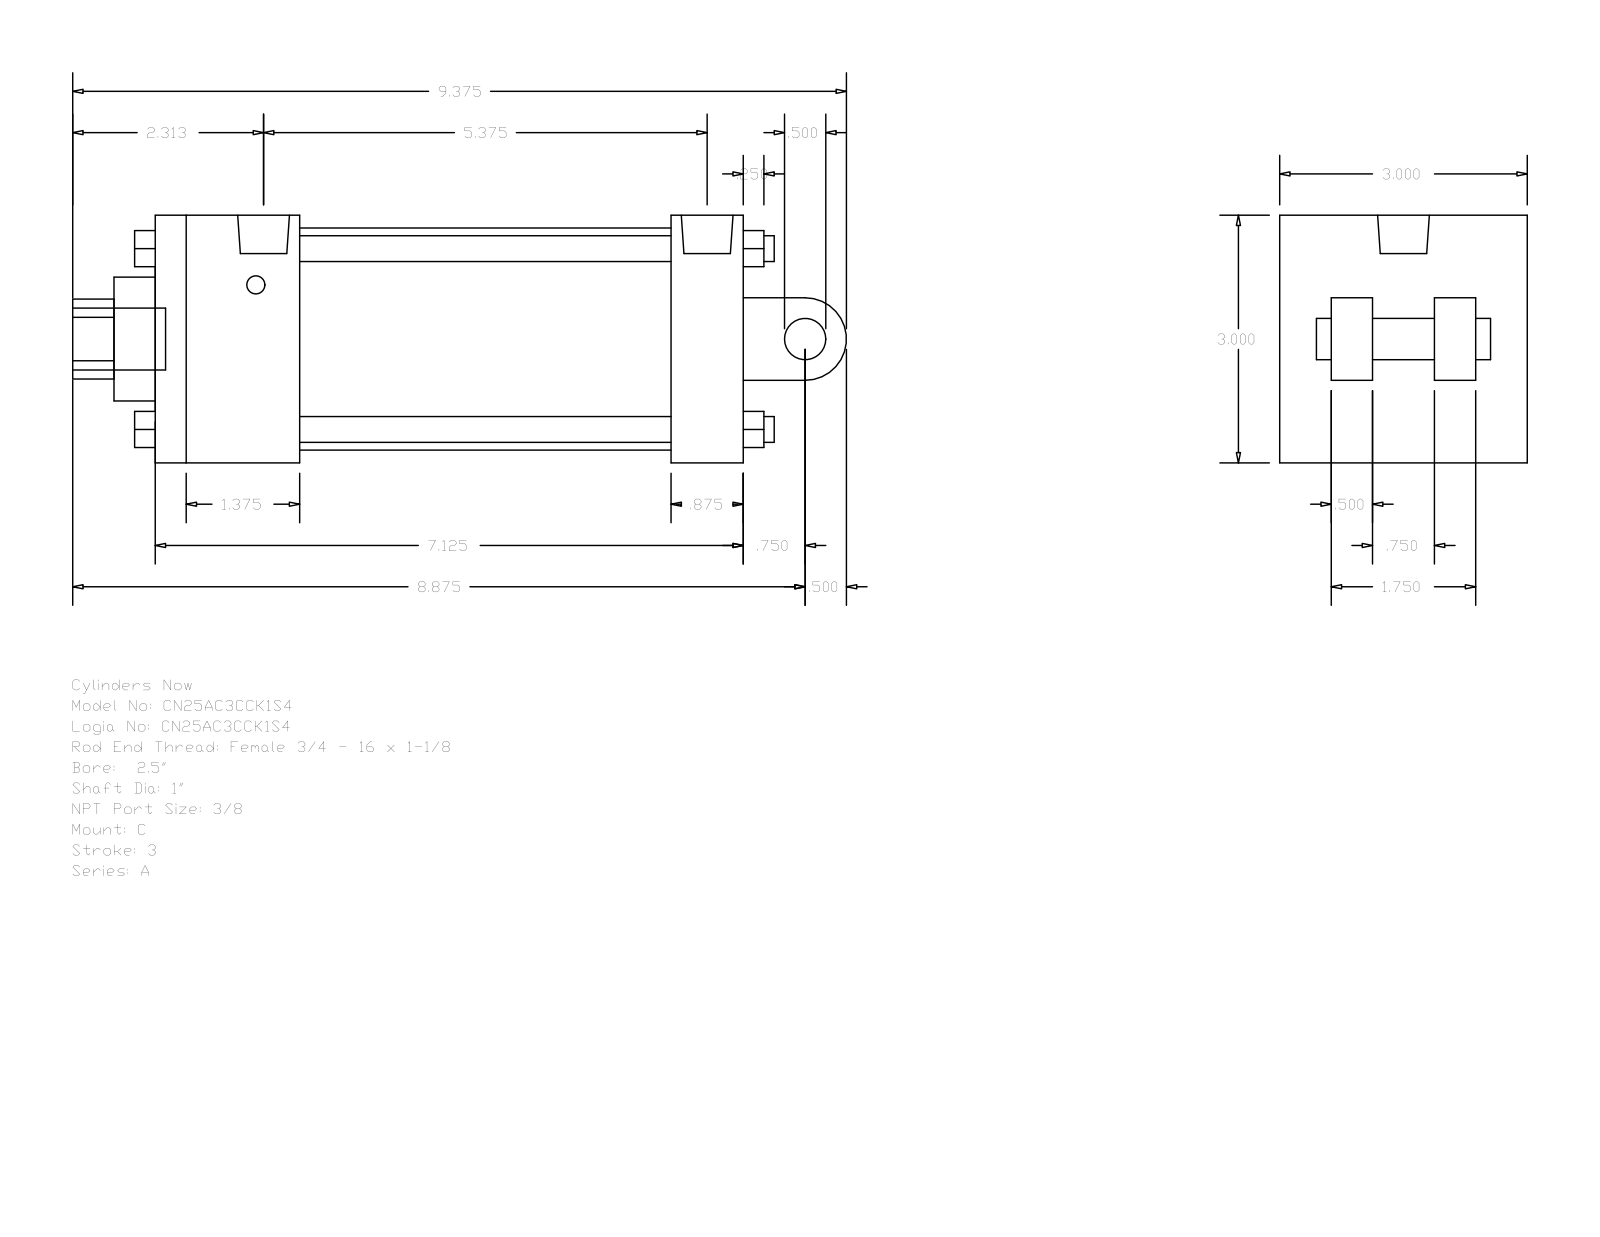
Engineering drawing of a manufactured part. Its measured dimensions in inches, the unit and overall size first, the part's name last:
Units: inches
Overall size (bounding box): 9.375 × 3 × 3
Round holes (diameter × count): ⌀0.219 ×2, ⌀0.627 ×1, ⌀1 ×1, ⌀1.5 ×1, ⌀2.69 ×1
Round bosses / shafts (diameter × count): ⌀0.313 ×4, ⌀0.219 ×2, ⌀0.75 ×1, ⌀0.627 ×1, ⌀0.5 ×1
Partial cylindrical surfaces — rounded edges, fillets, slot ends (radius × count): R0.484 ×1, R0.5 ×1
Main face-to-face distances: 3, 7.125, 0.5, 1.75, 6.25, 4.5, 5.375, 0.875, 0.625, 1
Hole centre spacings: 0.094
Bodies: 0 solids, 135 faces (102 planar, 33 cylindrical, 0 other)
Part name (STEP PRODUCT): A_C__0250_1
STEP written by: GSSL Pune (CONFIG_CONTROL_DESIGN)
